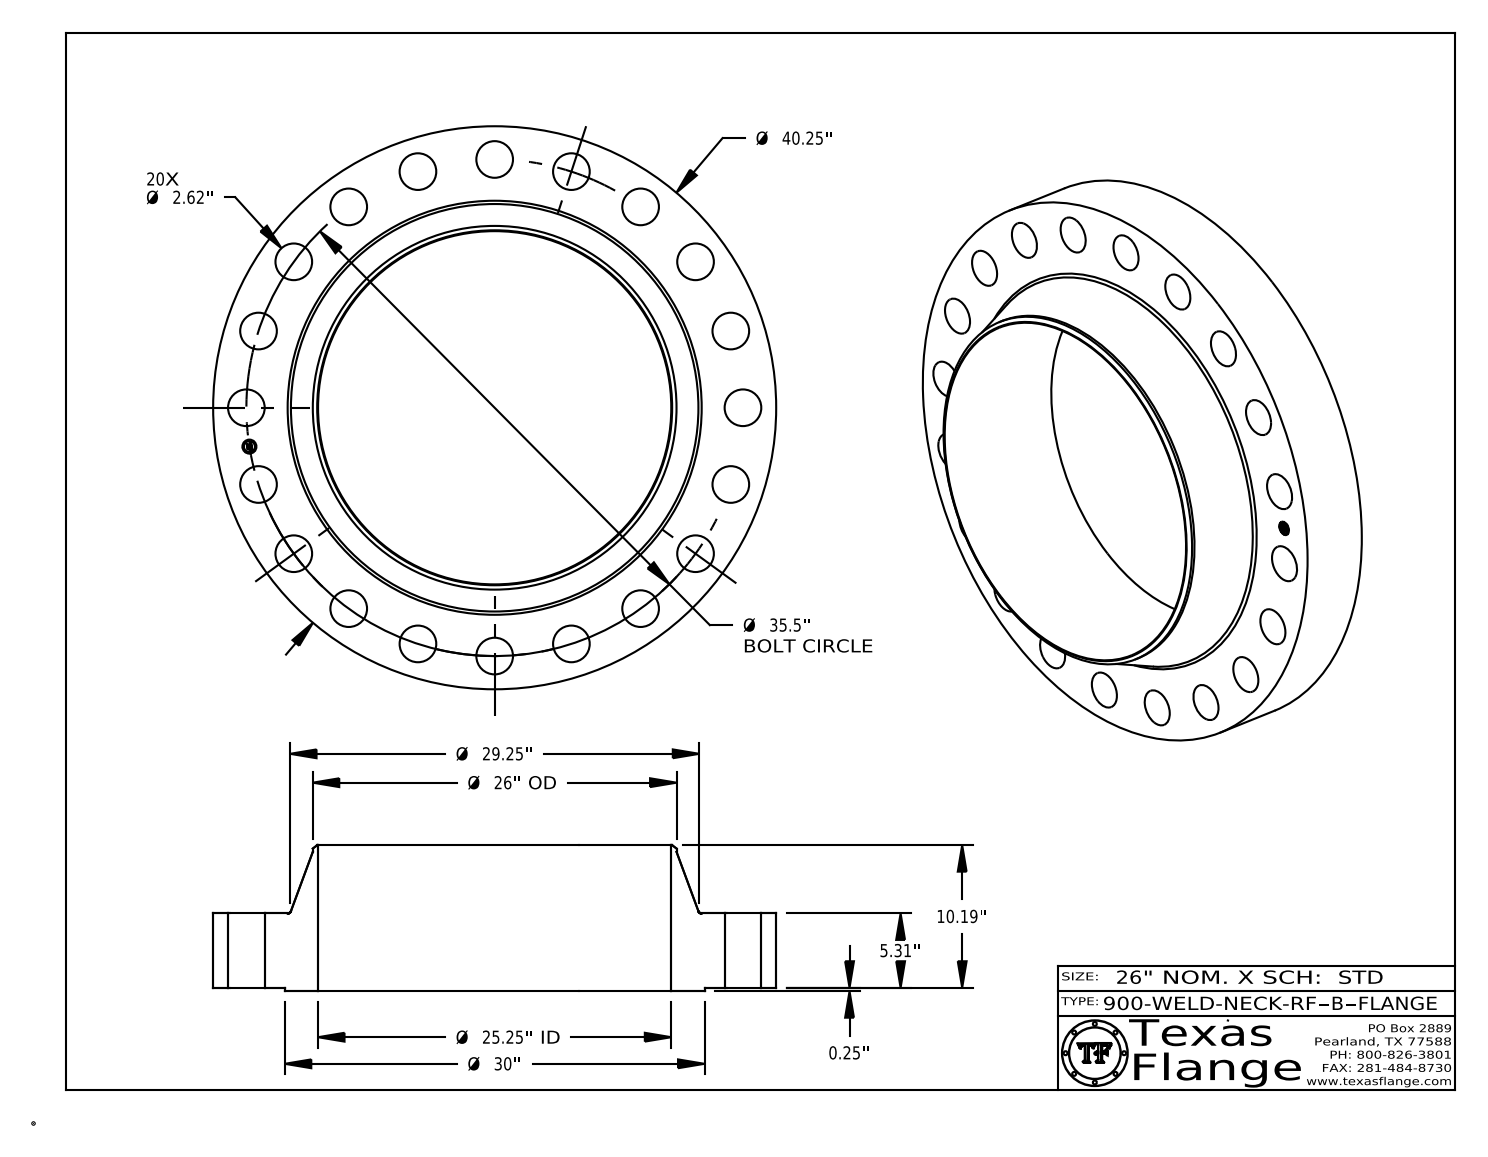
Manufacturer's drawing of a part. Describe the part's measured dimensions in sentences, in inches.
The part is named "900-WELD-NECK-RF, Series B". Its 3-D file was written by "CATIA V5 STEP AP214 (AUTOMOTIVE_DESIGN)". It is 1 solid with 443 faces: 369 planar, 68 cylindrical and 6 other. Overall it measures 40.25 by 40.25 by 10.44 inches. Its volume is 4 026 cubic inches and its surface area 4 013 square inches. Round holes: 20 of diameter 2.62, 1 of diameter 1, 1 of diameter 25.25. Round bosses or shafts: 8 of diameter 0.061, 1 of diameter 40.25, 1 of diameter 30, 1 of diameter 26, 1 of diameter 0.788. The main face-to-face distances are 5.31, 0.25, 5.56, 10.44, 10.19, 4.88, 5.545, 5.295, 0.015, 4.895. The hole center spacings are 17.75, 10.97, 28.72, 31.631, 16.117, 20.866, 25.102, 33.762.
